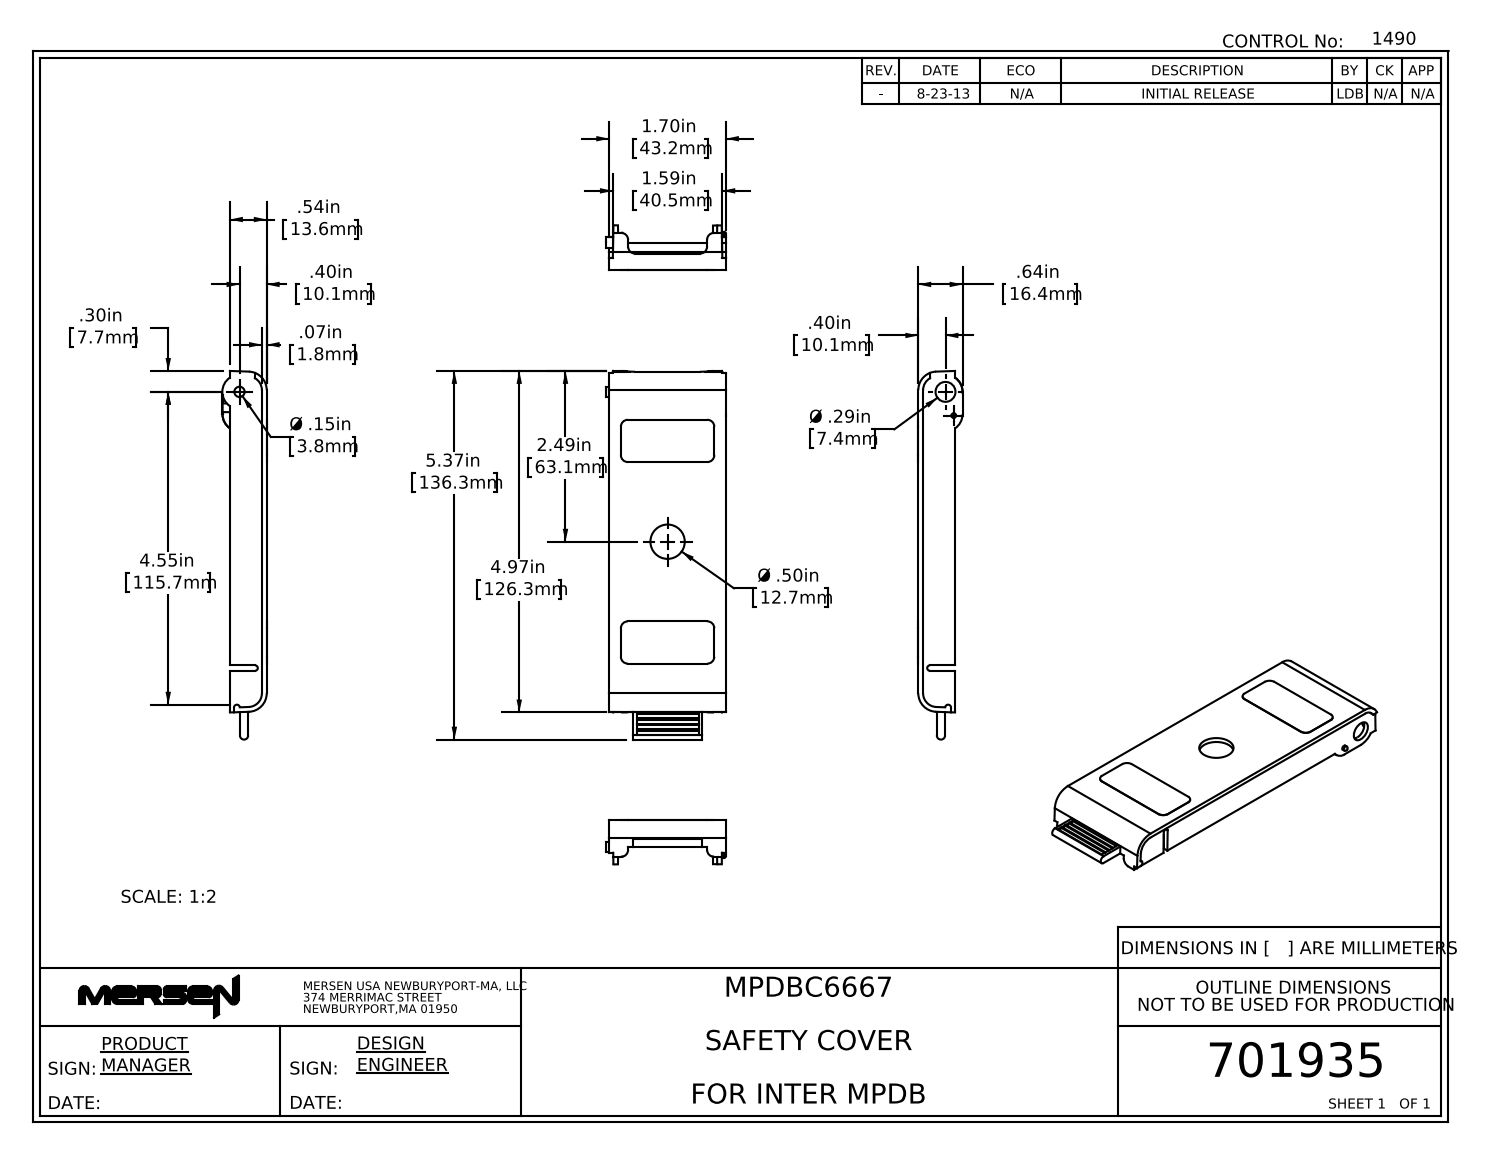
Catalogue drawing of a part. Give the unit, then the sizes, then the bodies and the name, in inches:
Units: inches
Overall size (bounding box): 5.367 × 1.751 × 0.647
Round holes (diameter × count): ⌀0.29 ×1, ⌀0.5 ×1
Round bosses / shafts (diameter × count): ⌀0.15 ×1, ⌀0.07 ×1
Partial cylindrical surfaces — rounded edges, fillets, slot ends (radius × count): R0.1 ×12, R0.03 ×8, R0.25 ×3, R0.2 ×2, R0.27 ×2, R0.04 ×1, R0.043 ×1, R0.06 ×1
Main face-to-face distances: 0.07, 1.511, 0.071, 0.465, 0.535, 0.536, 1.7, 0.145, 0.32, 0.39
Volume: 1.031 in³ · Surface area: 29.19 in²
Bodies: 1 solid, 132 faces (80 planar, 42 cylindrical, 10 other)
Part name (STEP PRODUCT): 330559rev
STEP written by: SolidWorks 2013 (AUTOMOTIVE_DESIGN)
